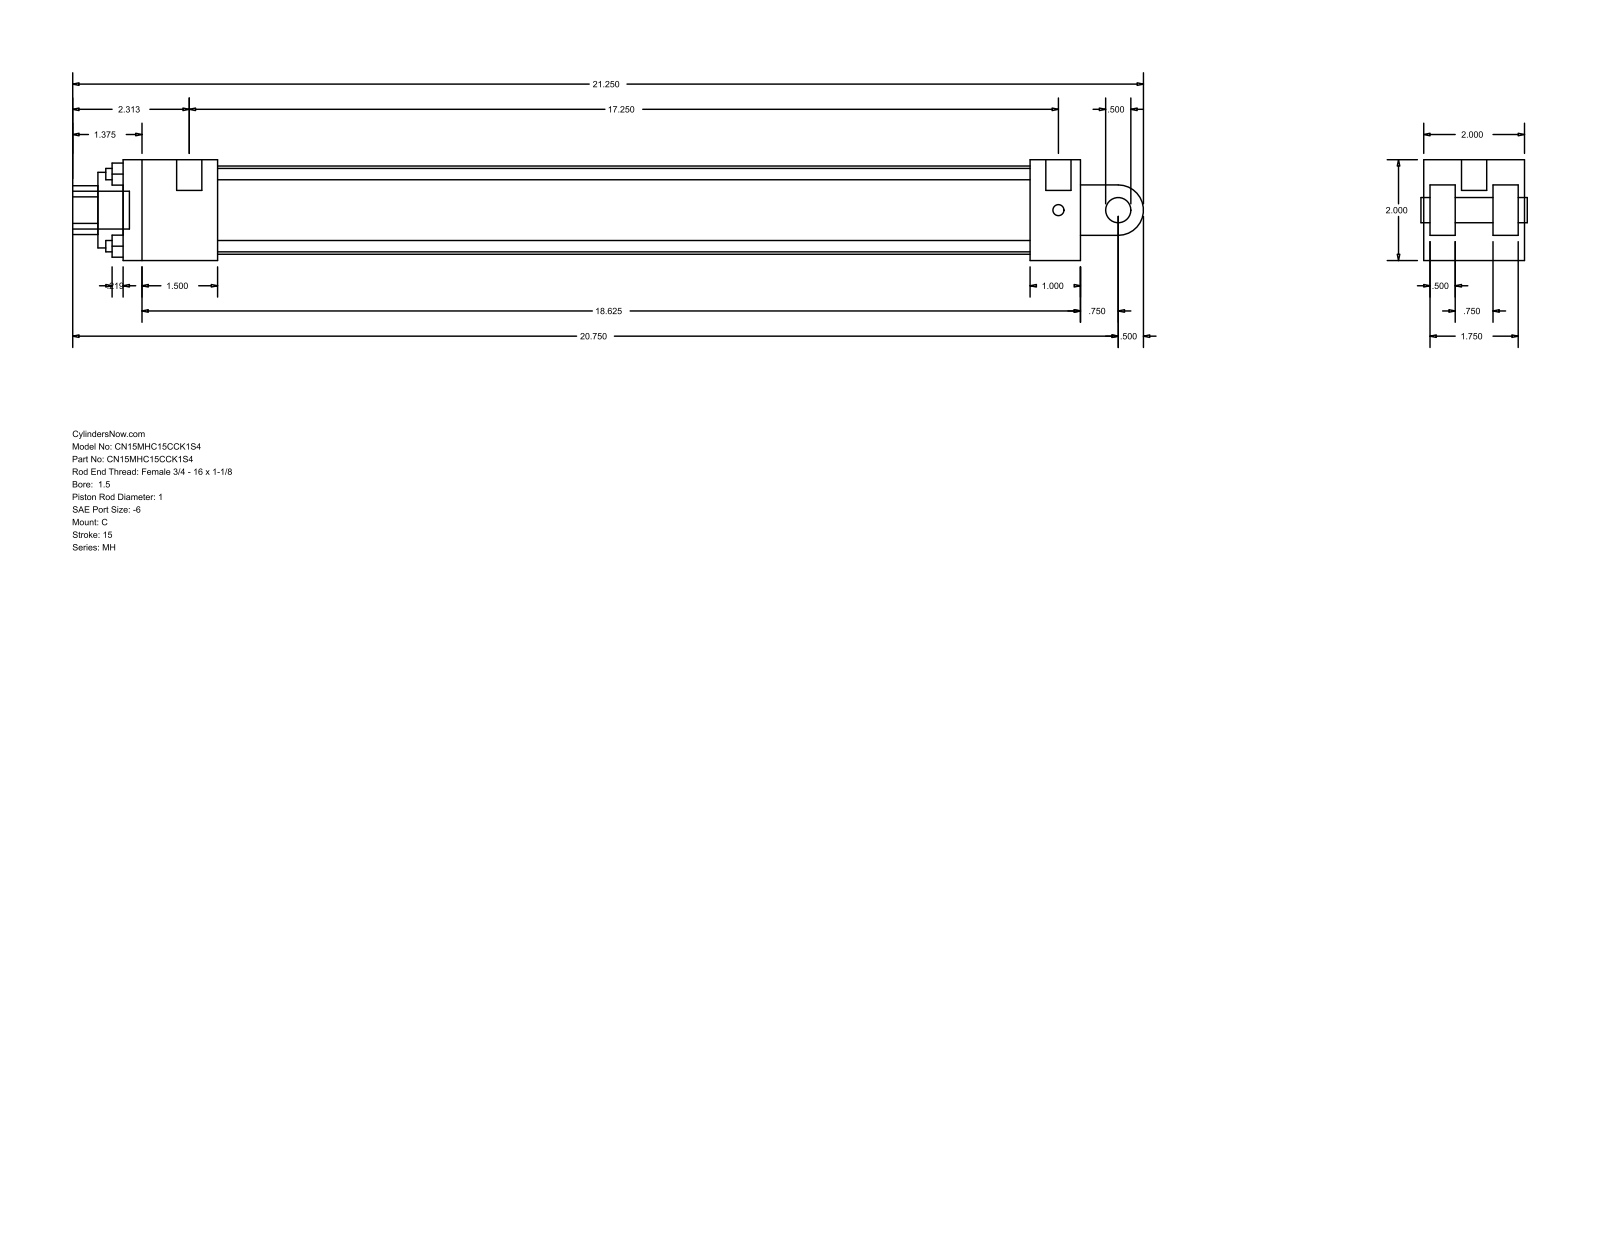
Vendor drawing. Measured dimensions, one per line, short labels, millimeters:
name: MH_C__0150_1
written by: GSSL Pune (CONFIG_CONTROL_DESIGN)
unit: mm
bodies: 0 solids, 99 faces (70 planar, 29 cylindrical, 0 other)
size: 539.75 × 50.8 × 50.8
holes: 4× ⌀5.71, 2× ⌀5.56, 1× ⌀12.7, 1× ⌀25.4, 1× ⌀38.1, 1× ⌀44.45
bosses: 2× ⌀12.7, 2× ⌀5.56, 1× ⌀19.05
rounds: 1× R12.29, 1× R12.7
face distances: 50.8, 12.7, 47.63, 3.17, 15.87, 25.4, 34.93, 31.76, 482.6, 38.1
hole spacings: 25.68, 36.32, 51.36
